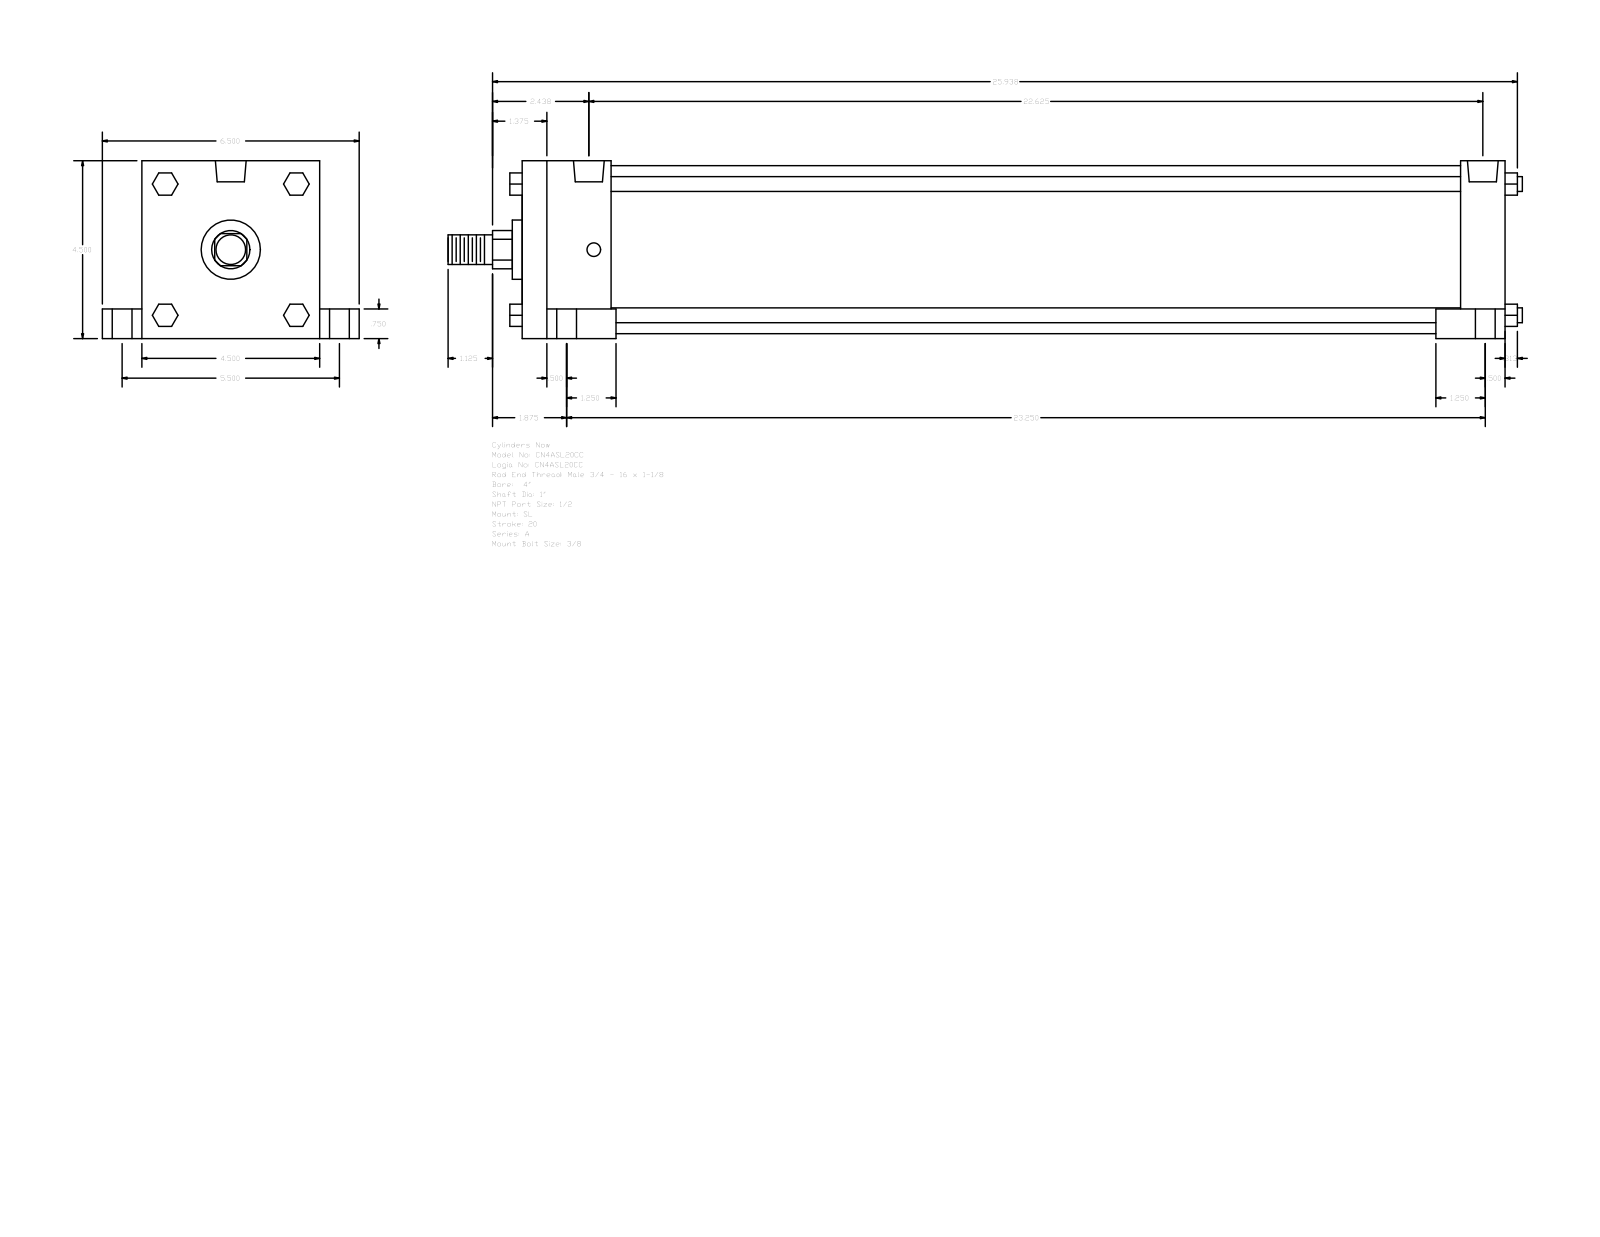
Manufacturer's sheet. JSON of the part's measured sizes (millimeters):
{"part_name": "A_SL__0400_1", "step_written_by": "GSSL Pune (CONFIG_CONTROL_DESIGN)", "units": "millimeters", "bodies": {"solids": 0, "faces": 150, "planar": 114, "cylindrical": 36, "other": 0}, "overall_size": [690.56, 165.1, 114.3], "round_holes": [[8.73, 4], [12.7, 4], [19.05, 4], [19.77, 2]], "round_bosses_or_shafts": [[9.53, 4], [107.95, 1], [38.1, 1], [25.4, 1], [19.05, 1]], "partial_cylinders_radius": [[12.29, 1]], "face_to_face_distances": [114.3, 631.83, 57.15, 574.68, 603.25, 546.1, 28.58, 19.05, 25.4, 139.7], "hole_center_spacings": [3.18, 69.87, 70.01, 71.3, 72, 139.7, 568.32, 571.5]}
